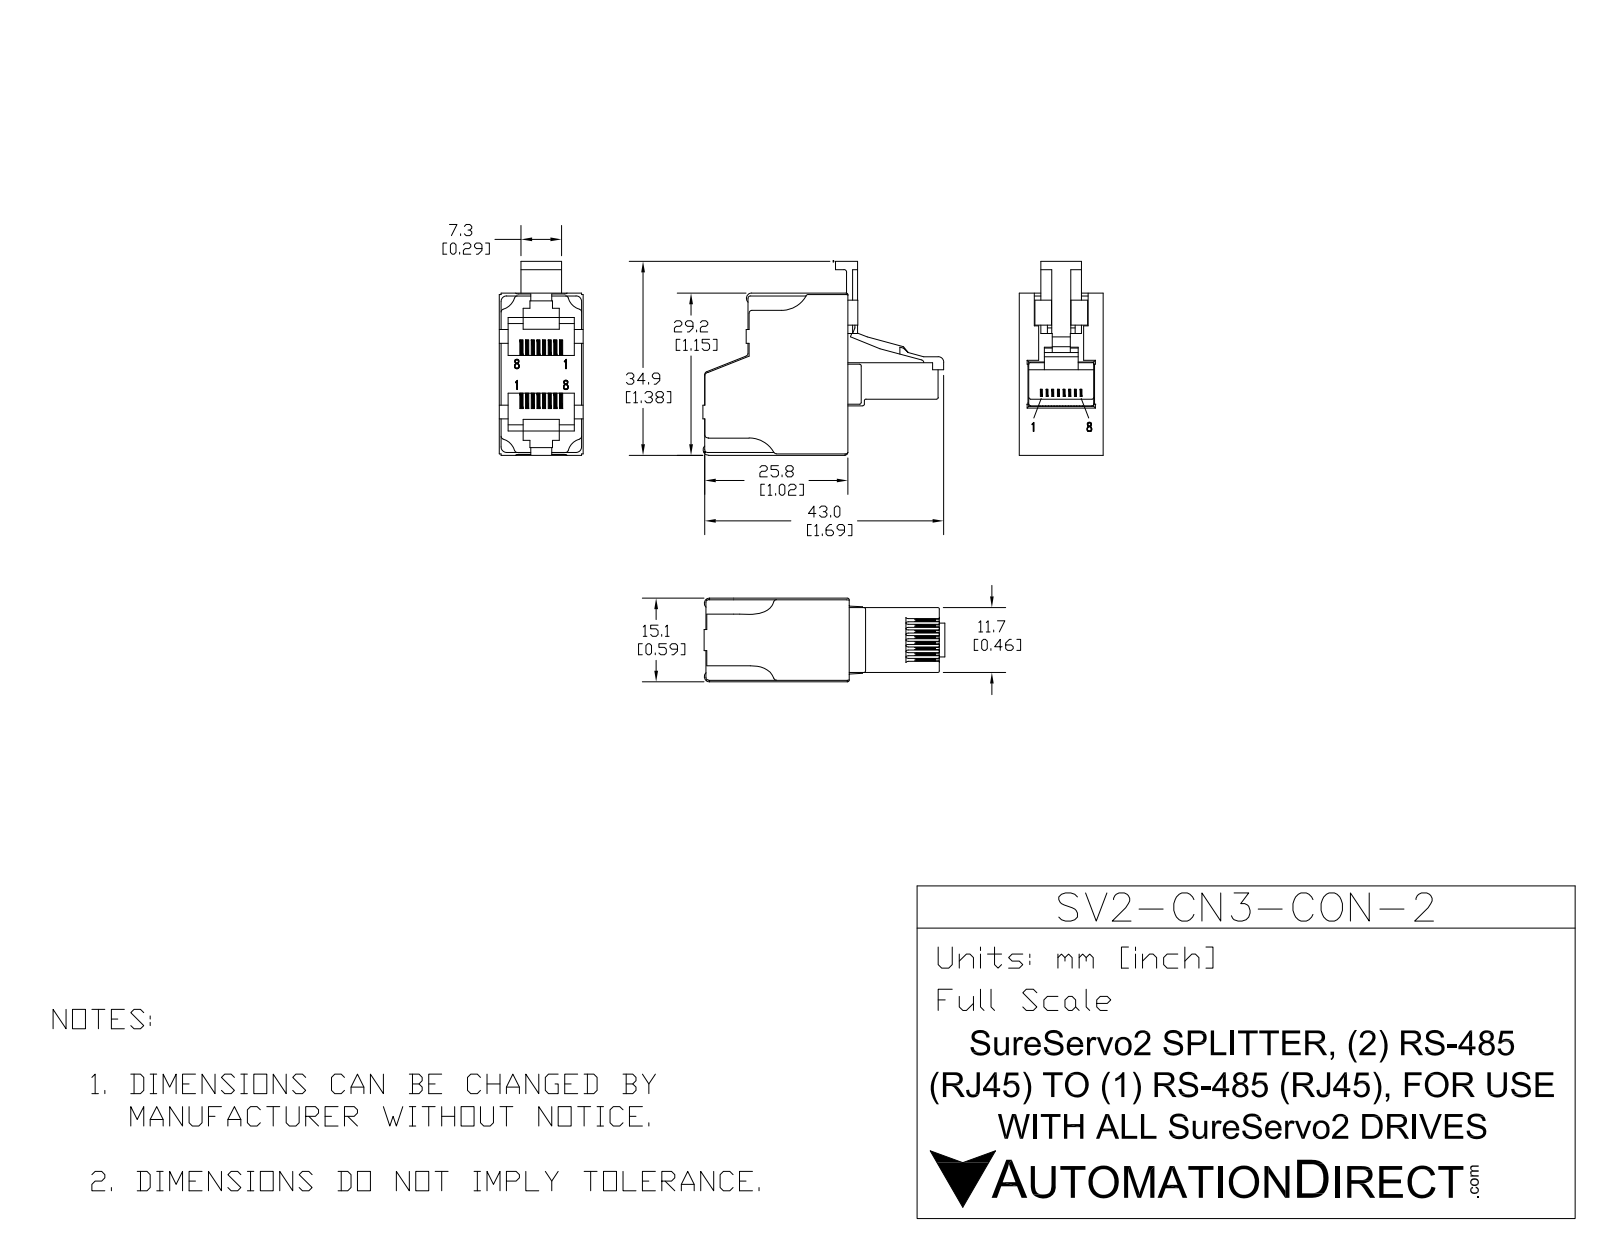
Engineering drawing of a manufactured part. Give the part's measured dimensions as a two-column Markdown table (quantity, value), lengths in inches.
| quantity | value |
| --- | --- |
| part name | SV2-CN3-CON-2 |
| STEP written by | SolidWorks 2017 (AUTOMOTIVE_DESIGN) |
| units | inches |
| bodies | 16 solids, 1885 faces (1204 planar, 499 cylindrical, 182 other) |
| overall size | 1.717 × 1.403 × 0.604 |
| volume | 0.362 in³ |
| surface area | 23.5 in² |
| round bosses / shafts (diameter × count) | 0.018 × 64 |
| partial cylindrical surfaces (radius × count) | 0.008 × 79, 0.02 × 59, 0.012 × 27, 0.014 × 18, 0.02 × 17, 0.039 × 11, 0.004 × 6, 0.016 × 6 |
| main face-to-face distances | 0.592, 0.017, 0.587, 0.576, 0.604, 0.58, 0.653, 0.571, 0.52, 0.047 |
